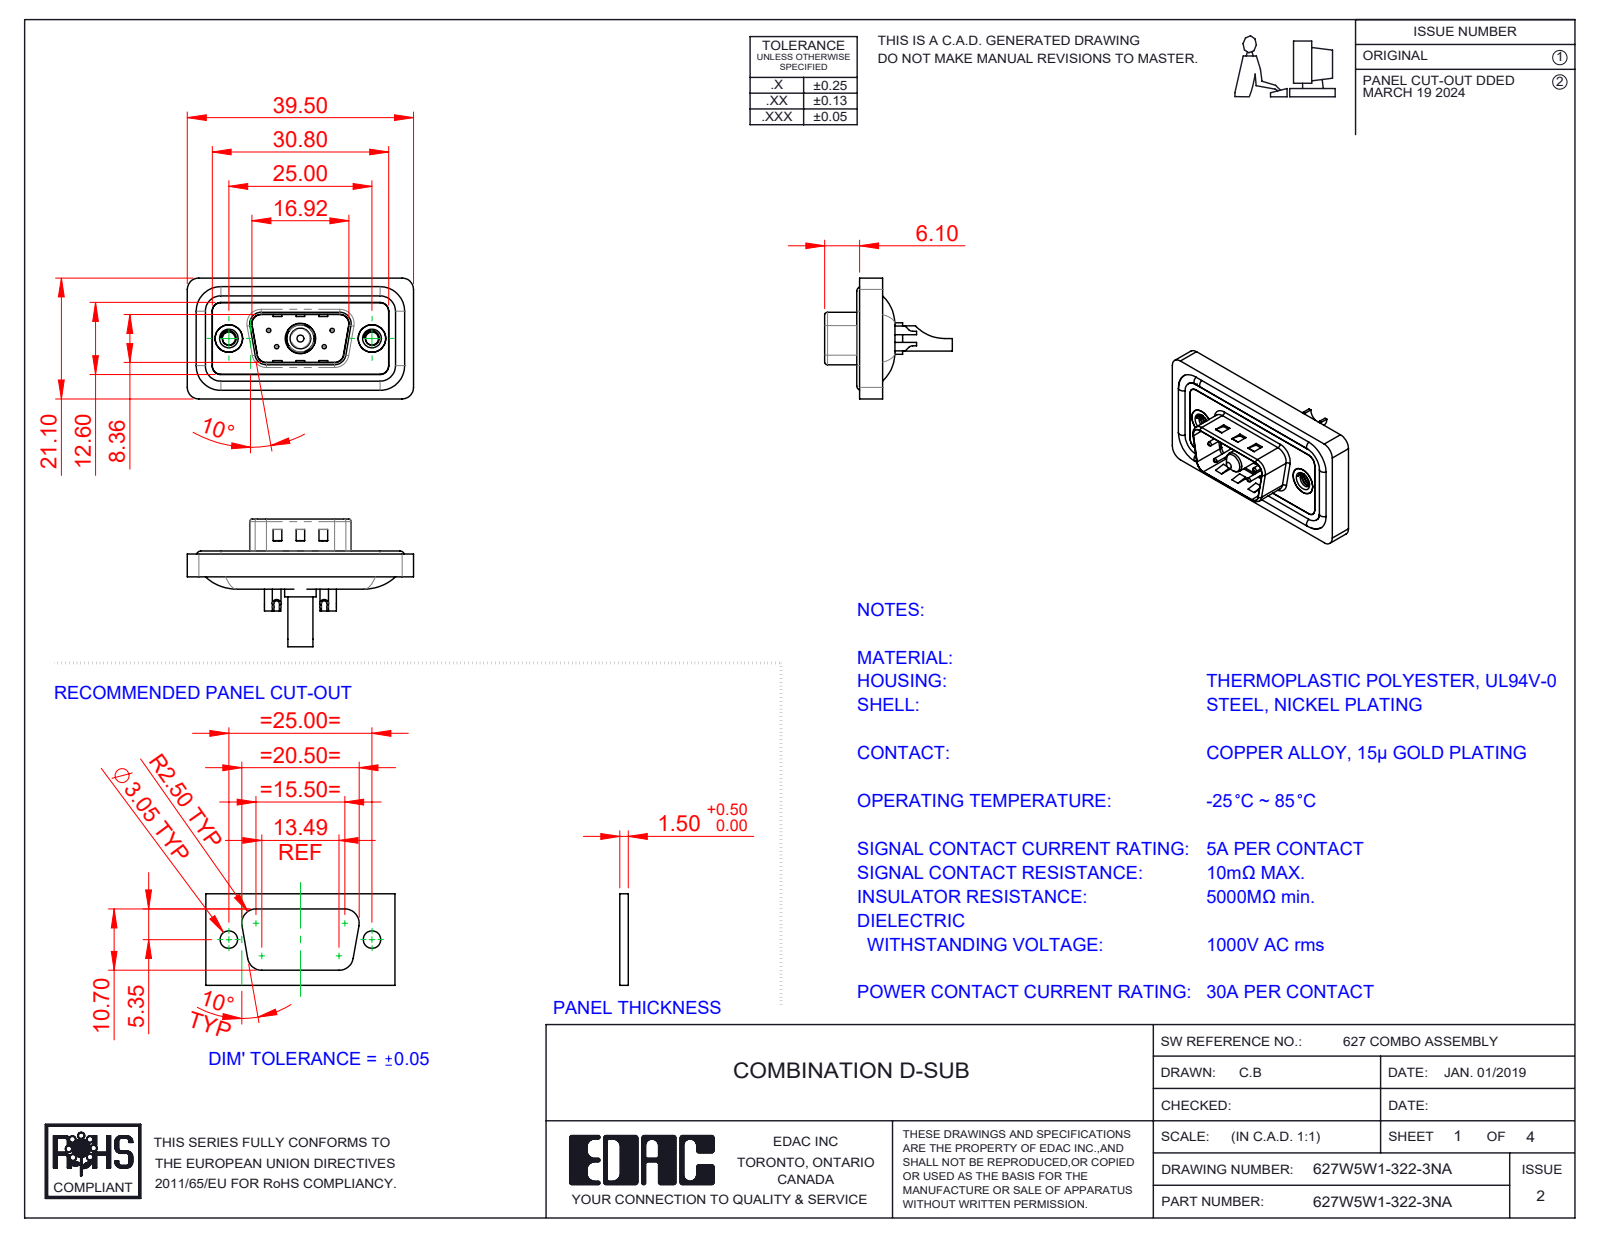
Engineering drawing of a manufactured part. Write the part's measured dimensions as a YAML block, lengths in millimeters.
part_name: "627W5W1-322-3NA; 627Combo Shell Rear_09 Contacts; 627Combo Shell Front_09 Contacts; 627Combo Contact Row 1_22 (+5 more)"
step_written_by: "SolidWorks 2023 (CONFIG_CONTROL_DESIGN)"
units: millimeters
bodies: {solids: 13, faces: 602, planar: 194, cylindrical: 268, other: 140}
overall_size: [39.5, 22.3, 21.1]
volume: 4419
surface_area: 7078
round_holes:
  - {diameter: 0.75, count: 4}
  - {diameter: 1, count: 4}
  - {diameter: 1.6, count: 4}
  - {diameter: 2, count: 4}
  - {diameter: 2.26, count: 2}
  - {diameter: 4, count: 2}
  - {diameter: 4.8, count: 2}
  - {diameter: 5, count: 2}
  - {diameter: 3.5, count: 1}
  - {diameter: 4.85, count: 1}
  - {diameter: 5.3, count: 1}
round_bosses_or_shafts:
  - {diameter: 1.6, count: 4}
  - {diameter: 1.5, count: 4}
  - {diameter: 4.9, count: 2}
  - {diameter: 5.5, count: 1}
  - {diameter: 5.2, count: 1}
  - {diameter: 4.75, count: 1}
  - {diameter: 4.4, count: 1}
  - {diameter: 3.75, count: 1}
partial_cylinders:
  - {radius: 1.5, count: 22}
  - {radius: 2, count: 18}
  - {radius: 0.5, count: 8}
  - {radius: 1.6, count: 8}
  - {radius: 1, count: 6}
  - {radius: 0.25, count: 4}
  - {radius: 0.6, count: 4}
  - {radius: 0.65, count: 4}
face_to_face_distances: [0.4, 1.1, 2.9, 1.6, 3.1, 0.5, 1.5, 2.5, 4, 0.8]
hole_center_spacings: [3.16, 5.72, 7.1, 12.5, 18.1, 4.39, 4.4, 8.31]
